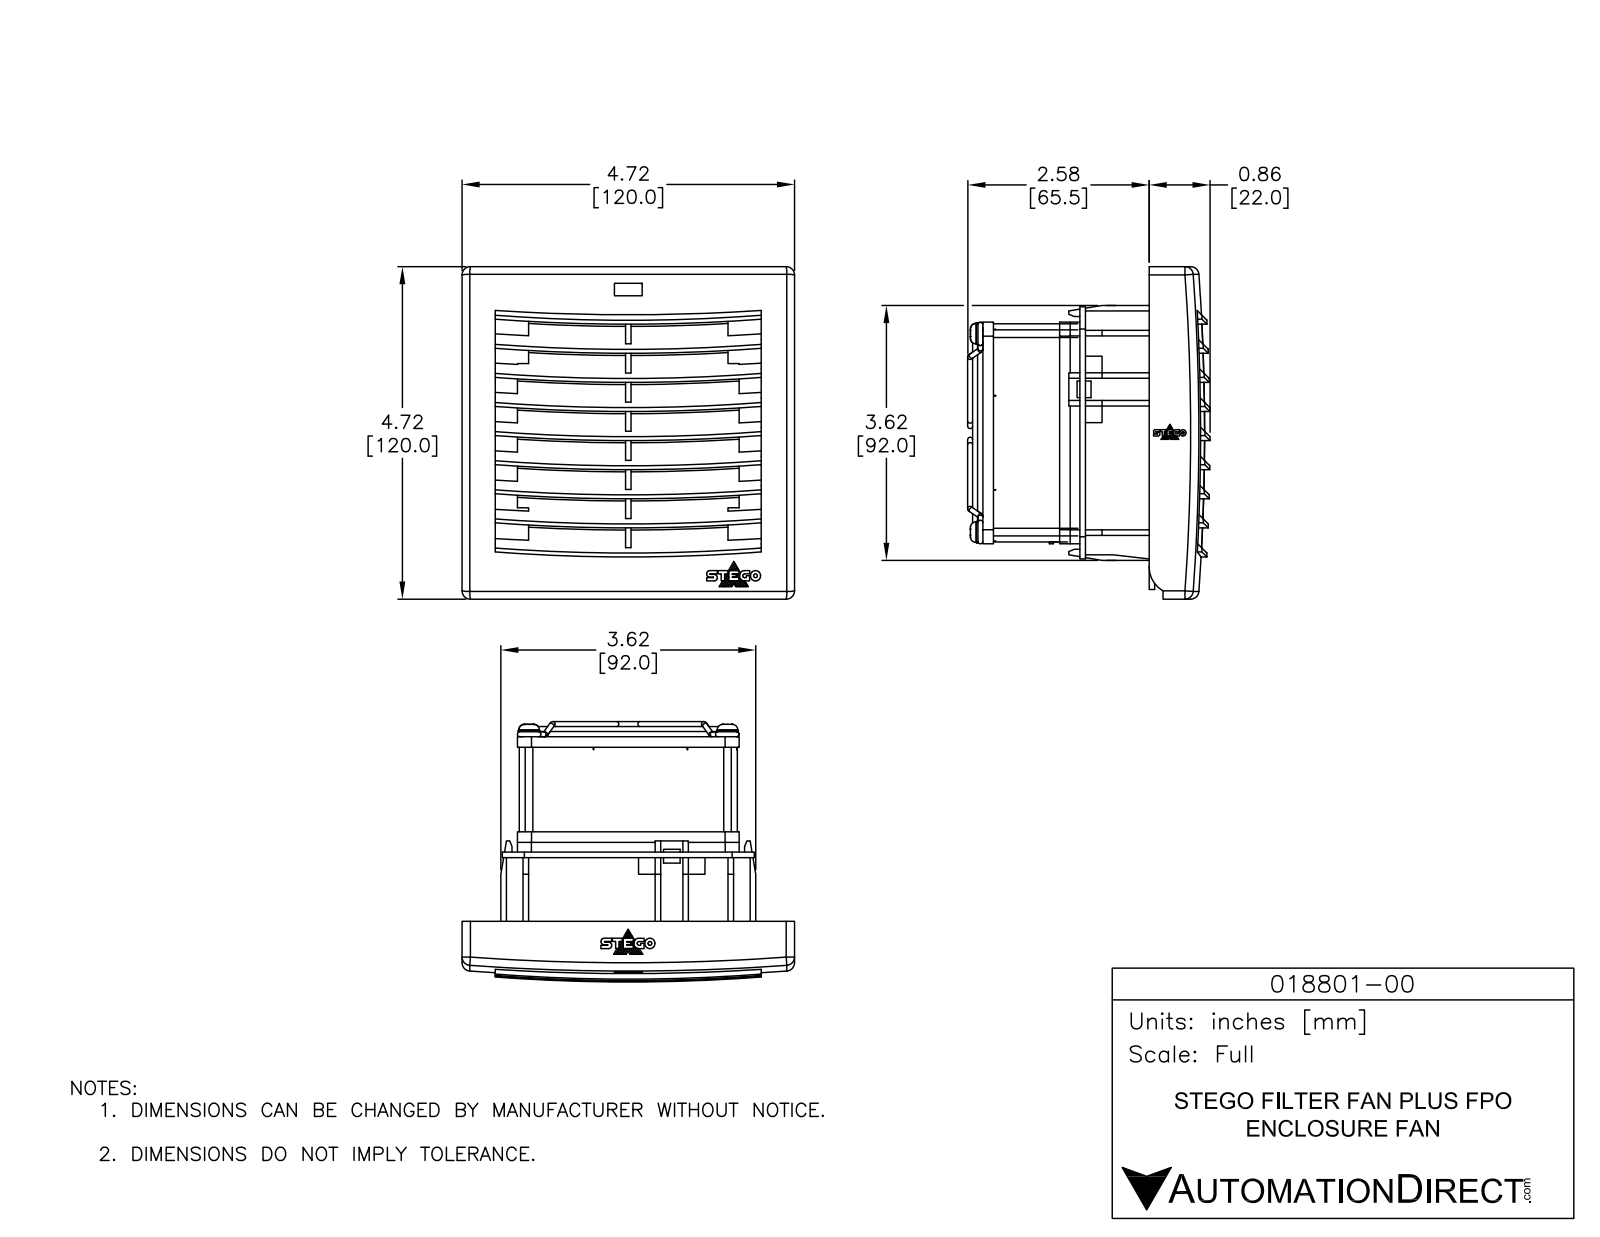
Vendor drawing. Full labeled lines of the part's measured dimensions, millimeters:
Part name (STEP PRODUCT): 018801-00
STEP written by: SolidWorks 2018 (AUTOMOTIVE_DESIGN)
Units: millimetres
Bodies: 1 solid, 506 faces (293 planar, 205 cylindrical, 8 other)
Overall size (bounding box): 120 × 120 × 95
Volume: 332 200 mm³ · Surface area: 143 500 mm²
Round holes (diameter × count): ⌀5.5 ×4, ⌀17 ×1, ⌀29.3 ×1, ⌀41.5 ×1, ⌀50.7 ×1, ⌀53.8 ×1, ⌀63.4 ×1, ⌀68 ×1, ⌀78.2 ×1
Round bosses / shafts (diameter × count): ⌀67.6 ×1, ⌀57.8 ×1, ⌀54.9 ×1, ⌀45.5 ×1, ⌀33.3 ×1, ⌀23.8 ×1, ⌀21 ×1
Partial cylindrical surfaces — rounded edges, fillets, slot ends (radius × count): R219.2 ×15, R33.3 ×5, R2.5 ×4, R3 ×4, R13.7 ×1, R19 ×1, R21.1 ×1, R43.6 ×1
Main face-to-face distances: 1.5, 8, 3, 2.3, 89.7, 16.1, 6.1, 9.5, 14, 16.3
Hole centre spacings: 52.9, 74.8, 105.8
